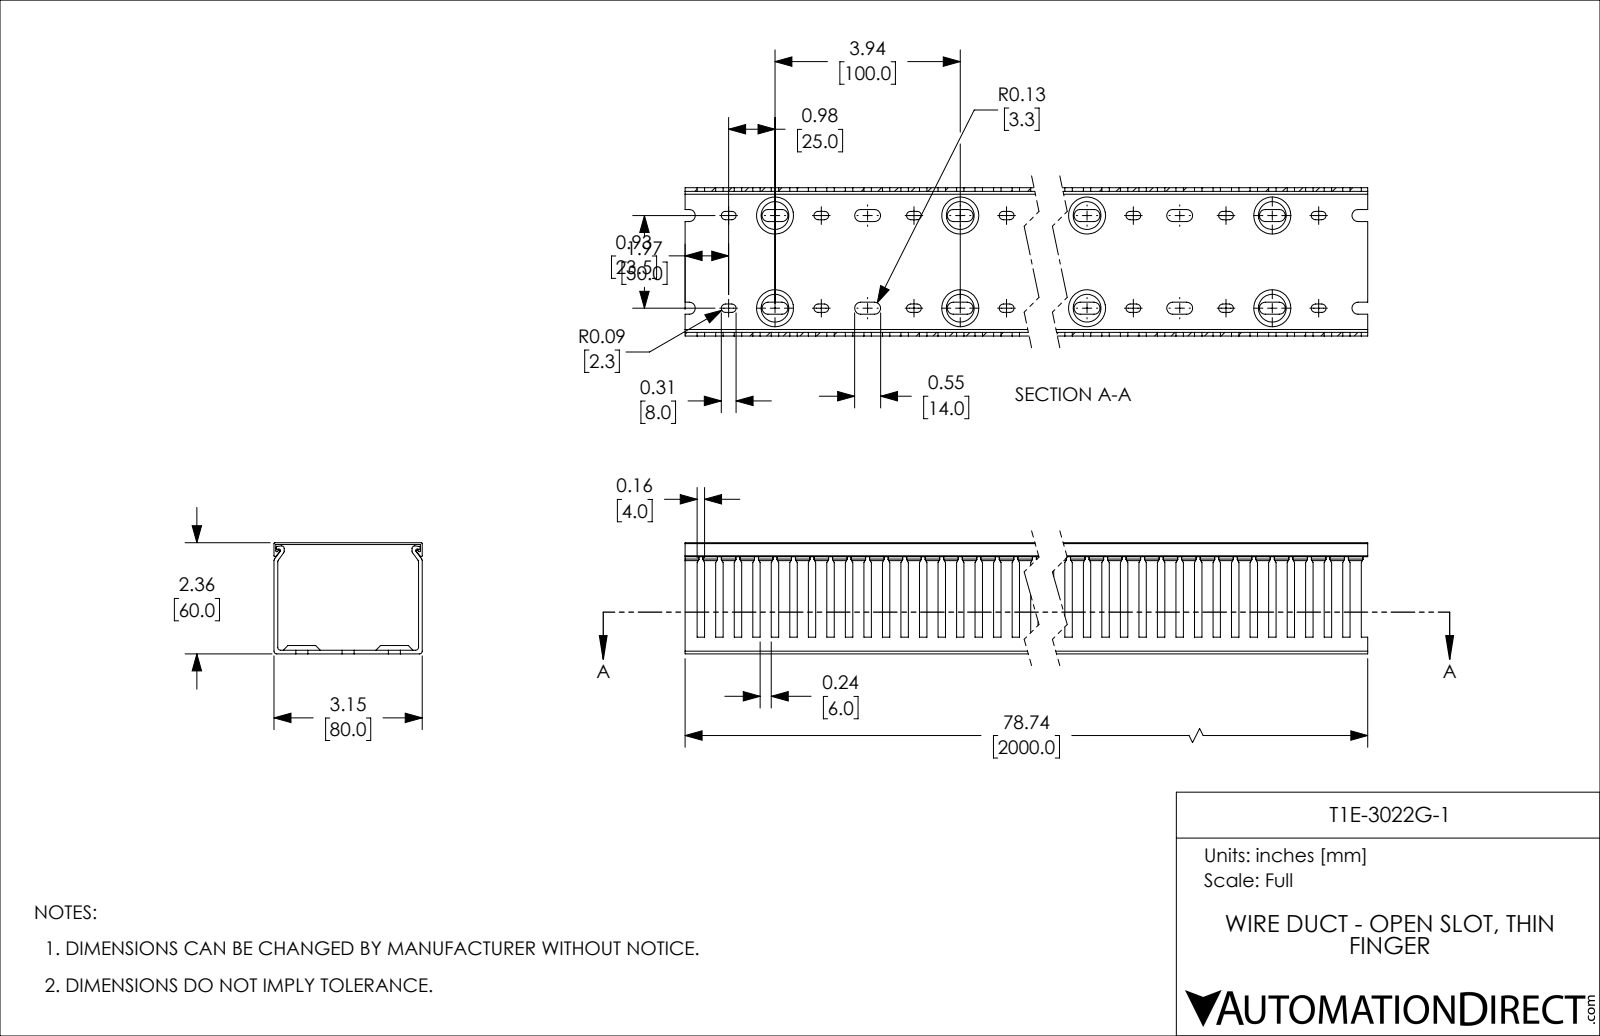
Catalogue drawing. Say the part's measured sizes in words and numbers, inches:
The part is named "T1E-3022G-1". Its 3-D file was written by "SolidWorks 2021 (CONFIG_CONTROL_DESIGN)". It is 2 solids with 1573 faces: 762 planar, 731 cylindrical and 80 other. Overall it measures 78.74 by 3.15 by 2.362 inches. Its volume is 59.64 cubic inches and its surface area 1 821 square inches. Partial cylindrical surfaces (rounded edges, fillets, slot ends): 200 of radius 0.128, 160 of radius 0.089, 12 of radius 0.059, 8 of radius 0.02, 6 of radius 0.03. The main face-to-face distances are 0.079, 3.071, 0.039, 2.362, 2.323, 2.244, 2.283, 3.15, 2.992, 3.11.
